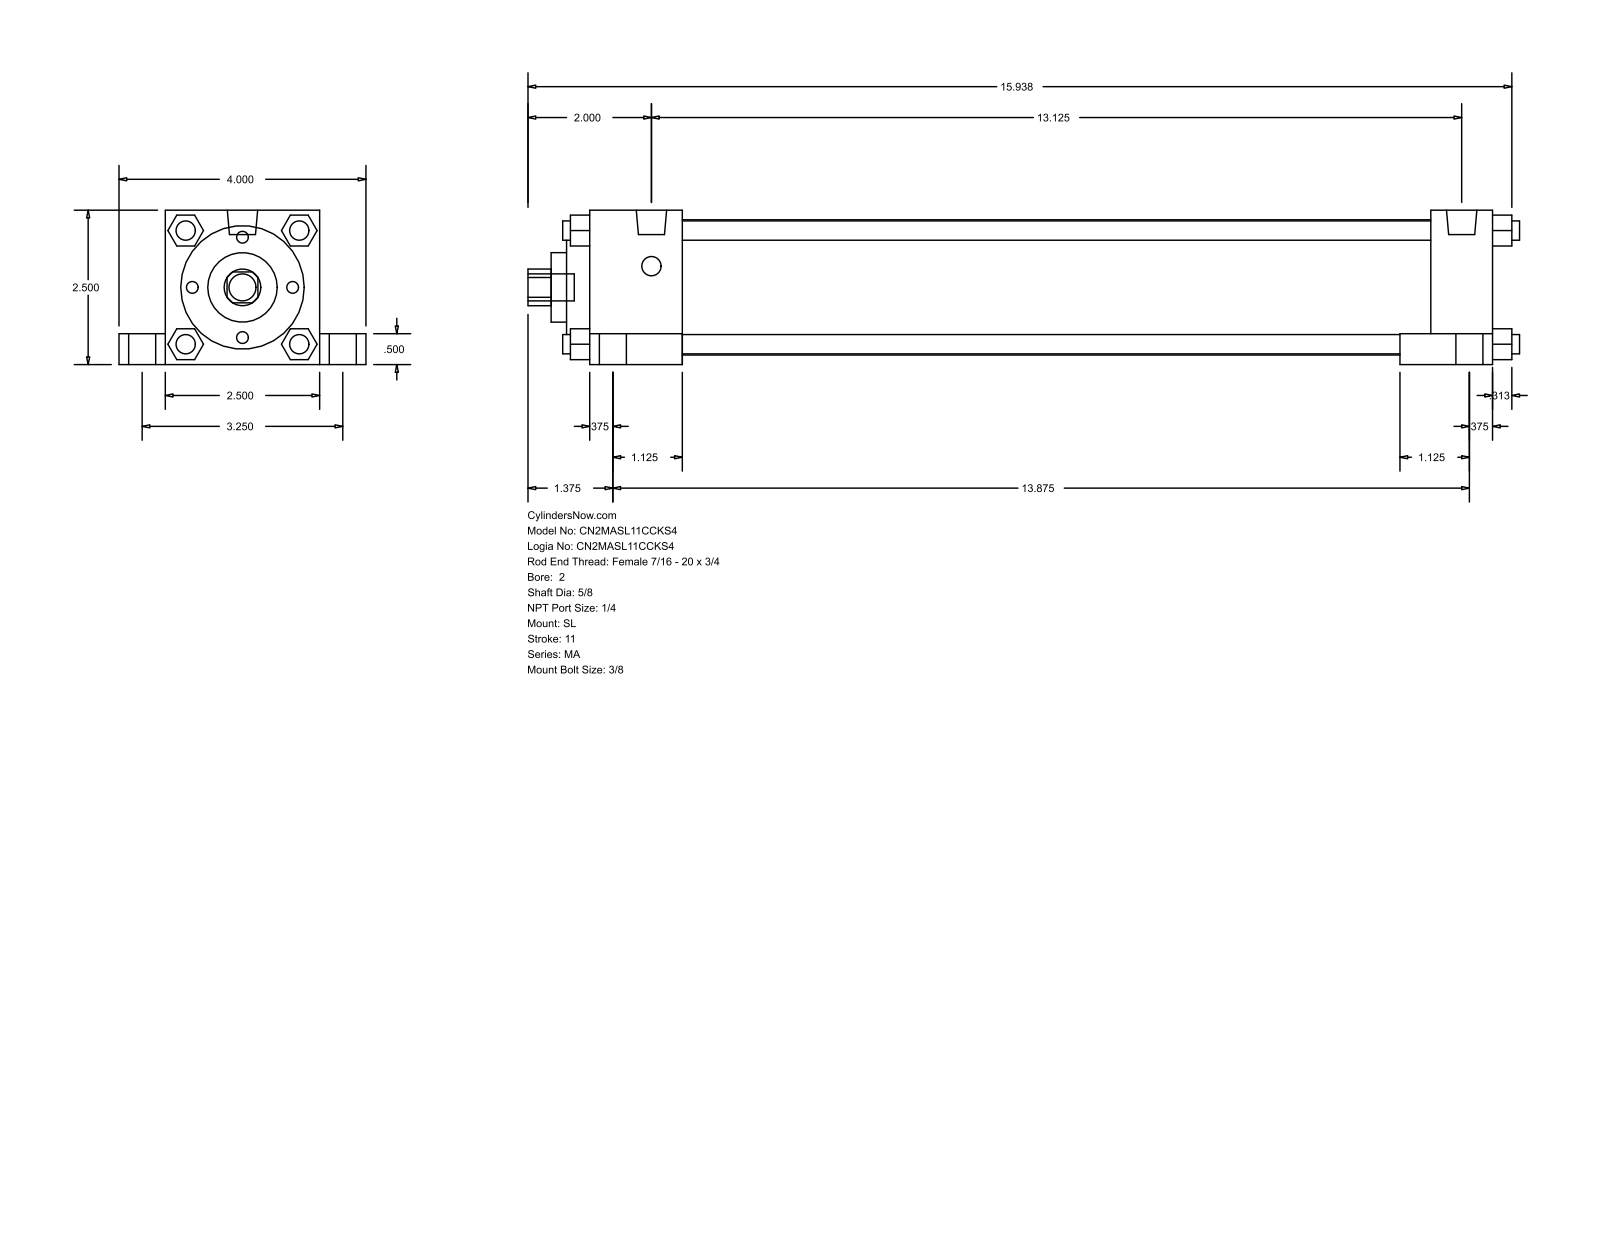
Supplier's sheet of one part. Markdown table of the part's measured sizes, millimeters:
| quantity | value |
| --- | --- |
| part name | MA_SL__0200_0.625 |
| STEP written by | GSSL Pune (CONFIG_CONTROL_DESIGN) |
| units | millimeters |
| bodies | 0 solids, 150 faces (113 planar, 37 cylindrical, 0 other) |
| overall size | 407.99 × 101.6 × 63.5 |
| round holes (diameter × count) | 15.88 × 1, 28.57 × 1, 50.8 × 1, 55.63 × 1 |
| round bosses / shafts (diameter × count) | 7.94 × 8, 11.11 × 5, 17.46 × 4, 12.49 × 2 |
| partial cylindrical surfaces (radius × count) | 7.54 × 1 |
| main face-to-face distances | 63.5, 12.7, 9.52, 25.4, 19.05, 82.55, 38.1, 371.48, 50.8, 333.38 |
